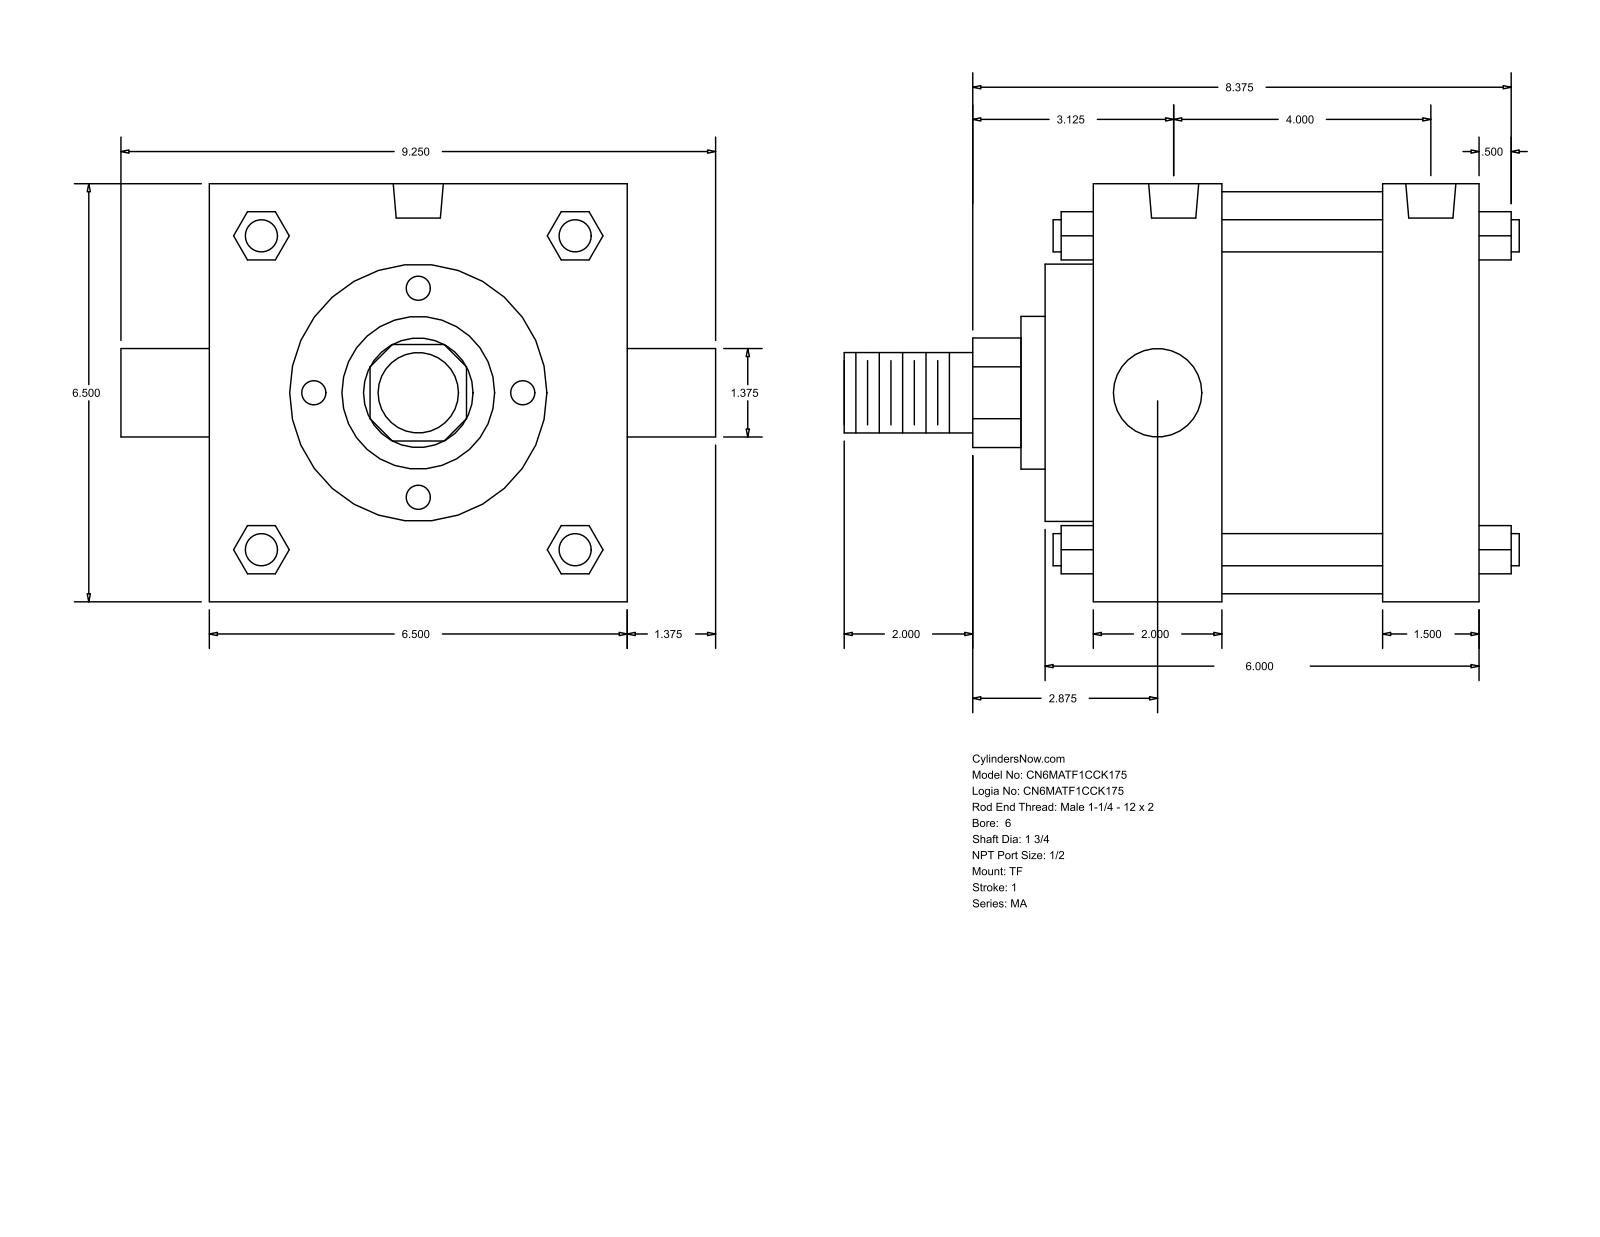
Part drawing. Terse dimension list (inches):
name: MA_TF__0600_1.75
written by: GSSL Pune (CONFIG_CONTROL_DESIGN)
unit: in
bodies: 0 solids, 122 faces (93 planar, 29 cylindrical, 0 other)
size: 10.5 × 9.25 × 6.5
holes: 3× ⌀0.687, 2× ⌀0.778
bosses: 4× ⌀0.5, 1× ⌀6.25, 1× ⌀4, 1× ⌀2.375, 1× ⌀1.75, 1× ⌀1.375, 1× ⌀1.25
rounds: 1× R0.852
face distances: 6.5, 6, 0.75, 1.5, 2, 4, 4.5, 2.5, 2.75, 5.25
hole spacings: 4
